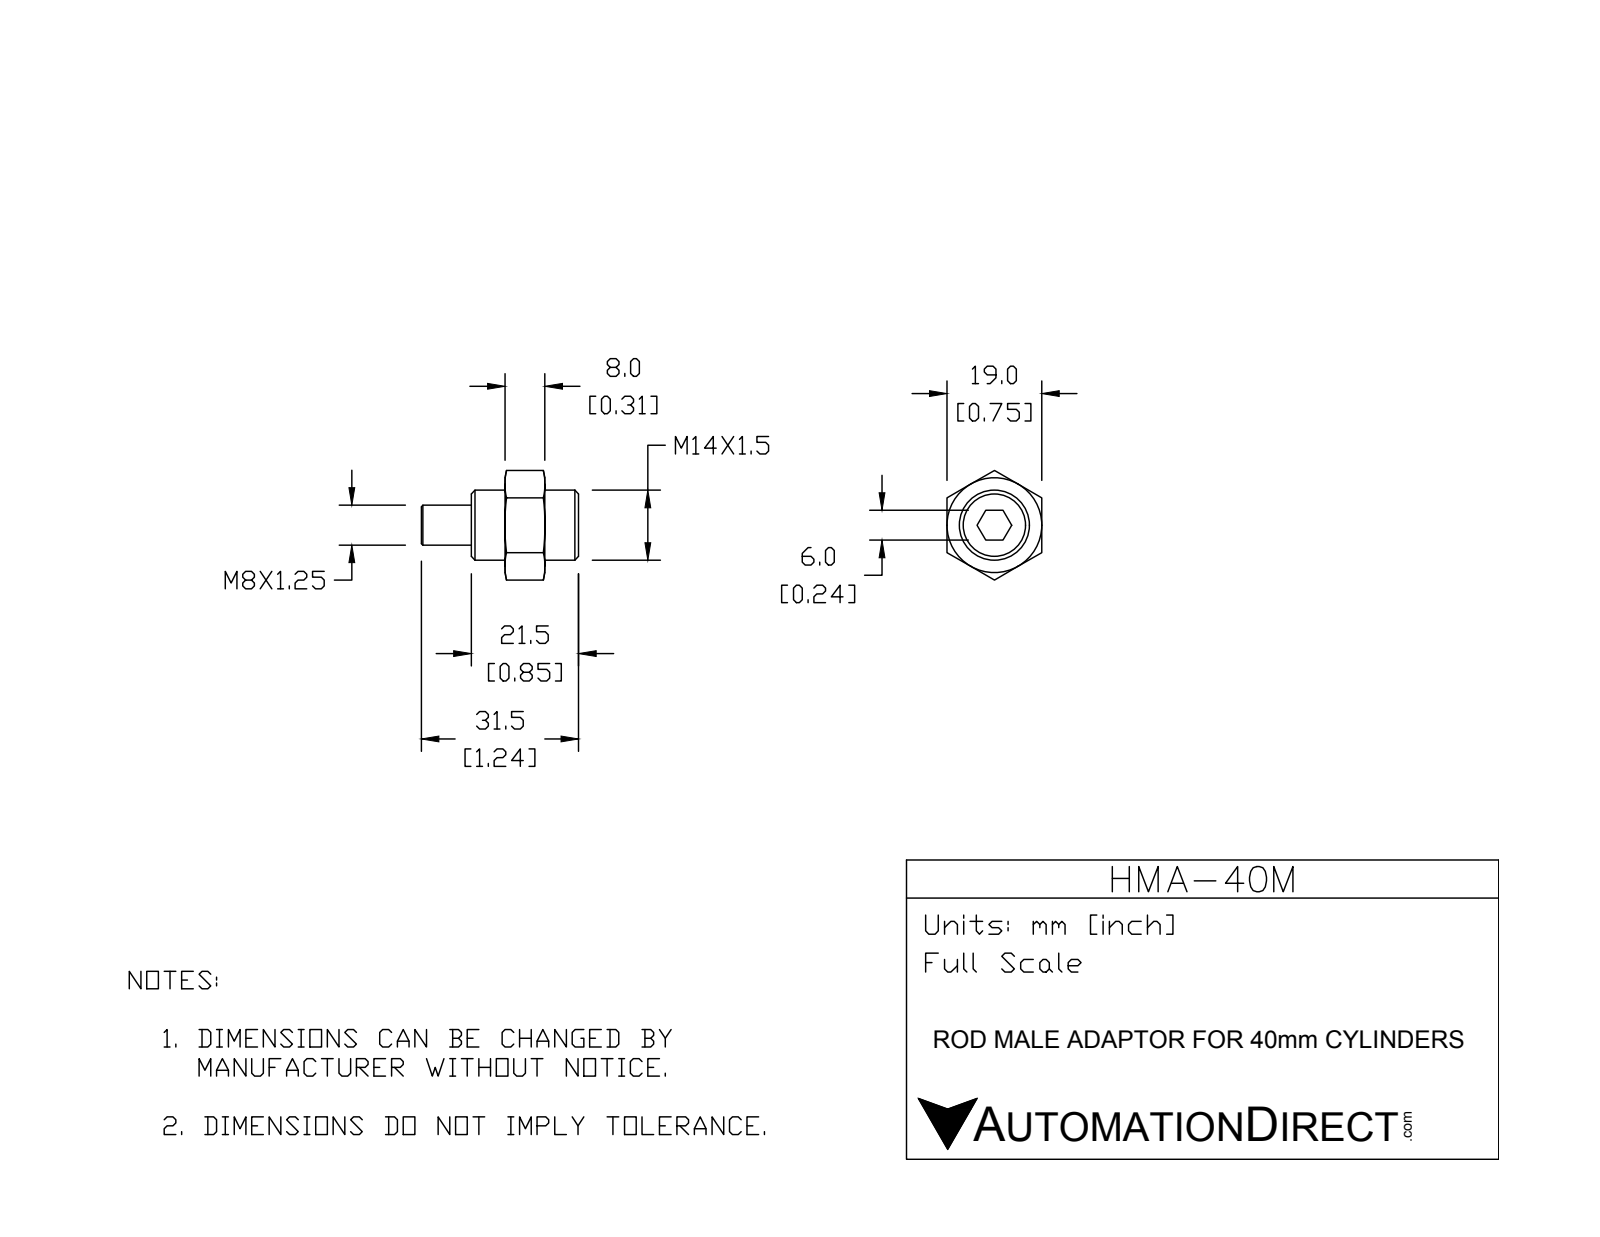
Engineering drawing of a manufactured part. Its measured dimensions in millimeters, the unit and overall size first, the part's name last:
Units: millimetres
Overall size (bounding box): 31.5 × 21.94 × 19
Round holes (diameter × count): ⌀14 ×1
Round bosses / shafts (diameter × count): ⌀8 ×1
Main face-to-face distances: 19, 6.75, 14.75, 8, 21.5, 6, 31.5, 24.75, 16.75, 10
Volume: 4 879 mm³ · Surface area: 2 757 mm²
Bodies: 2 solids, 44 faces (18 planar, 6 cylindrical, 20 other)
Part name (STEP PRODUCT): HMA-40M
STEP written by: SolidWorks 2015 (CONFIG_CONTROL_DESIGN)
